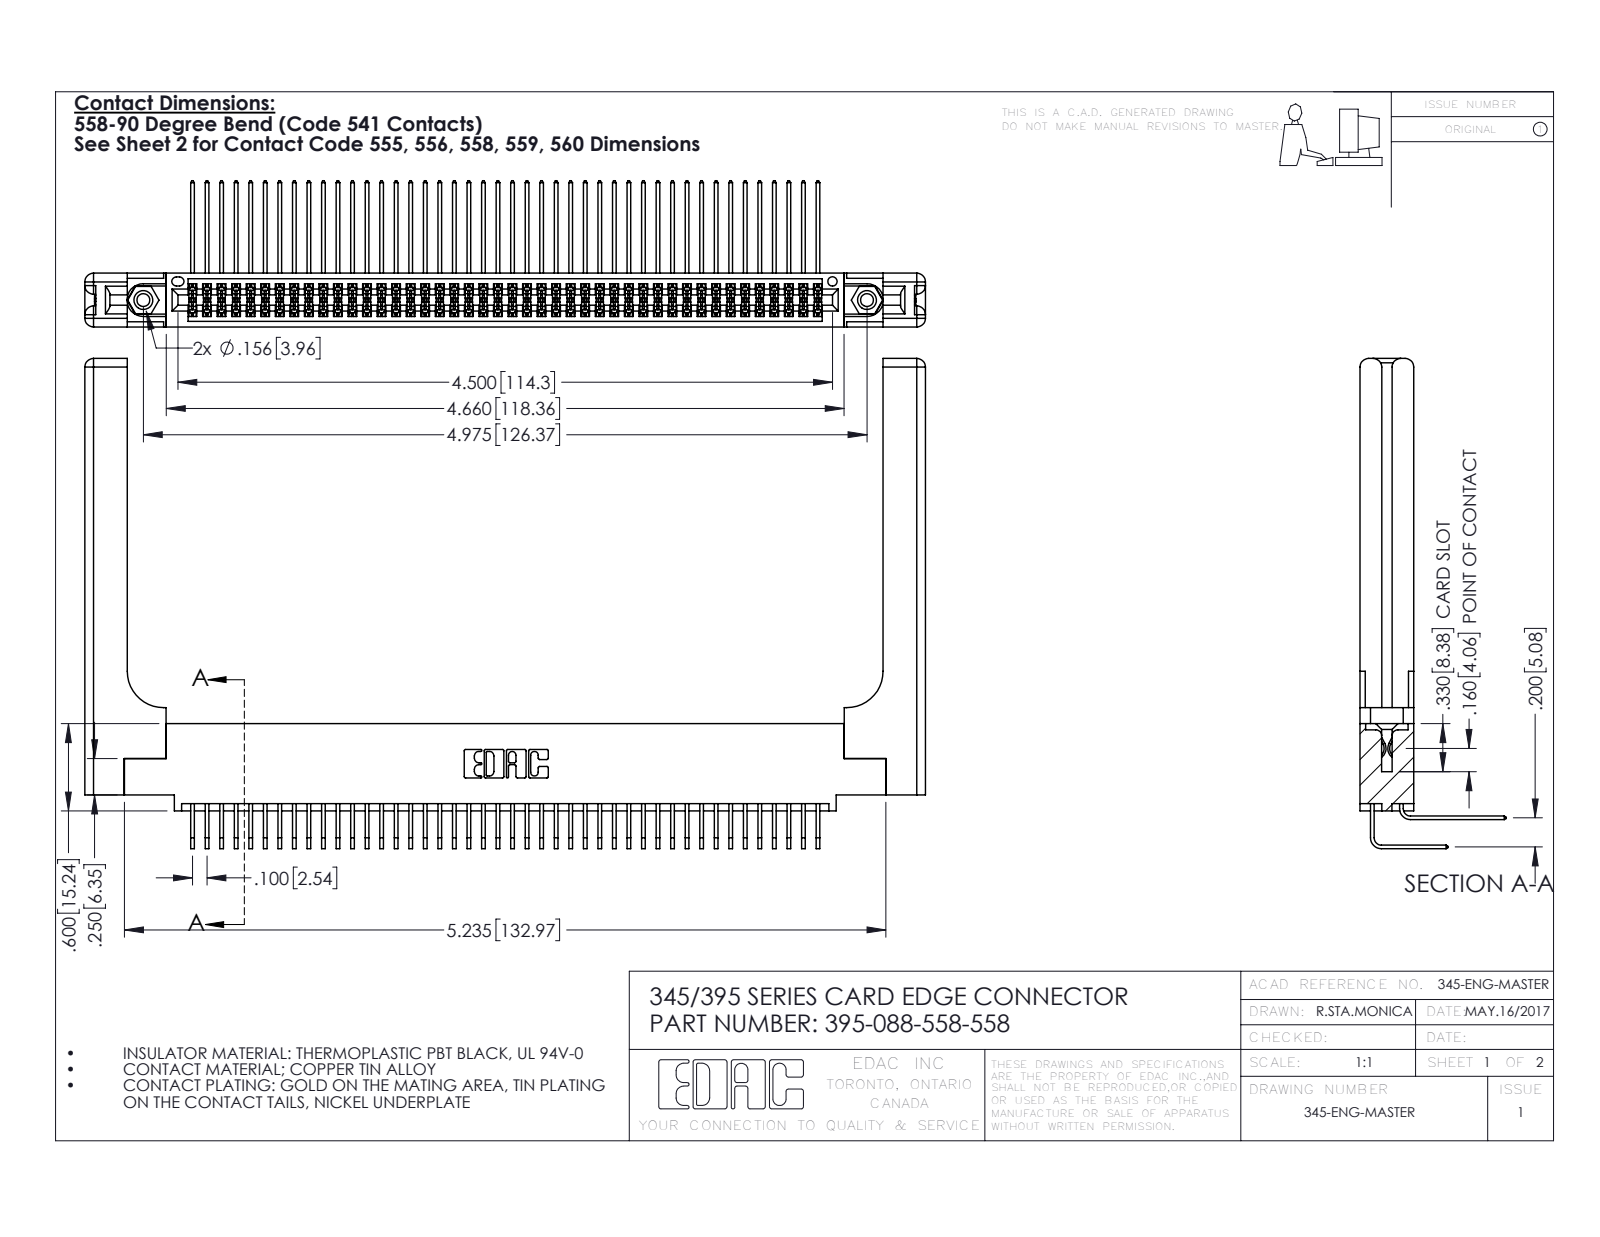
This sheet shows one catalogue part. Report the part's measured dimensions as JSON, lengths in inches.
{"part_name": "395-088-558-558; 345 Part_0.110 Offset - 0.156 Dia-TH; 345-250-001_345-250-001-102; 345-292-001_558 Tail - 2 (+2 more)", "step_written_by": "SolidWorks 2016 (CONFIG_CONTROL_DESIGN)", "units": "inches", "bodies": {"solids": 93, "faces": 4962, "planar": 3312, "cylindrical": 1590, "other": 60}, "overall_size": [5.779, 3.369, 1.005], "volume_in3": 1.415, "surface_area_in2": 45.45, "round_holes": [[0.089, 2], [0.125, 2], [0.156, 2], [0.064, 1]], "round_bosses_or_shafts": [[0.155, 2]], "partial_cylinders_radius": [[0.006, 133], [0.01, 22], [0.06, 16], [0.007, 6], [0.031, 6], [0.026, 3], [0.014, 2], [0.019, 2]], "face_to_face_distances": [0.072, 0.298, 0.37, 0.2, 0.098, 0.272, 0.025, 0.225, 0.148, 0.15], "hole_center_spacings": [0.27, 4.739, 4.975]}
